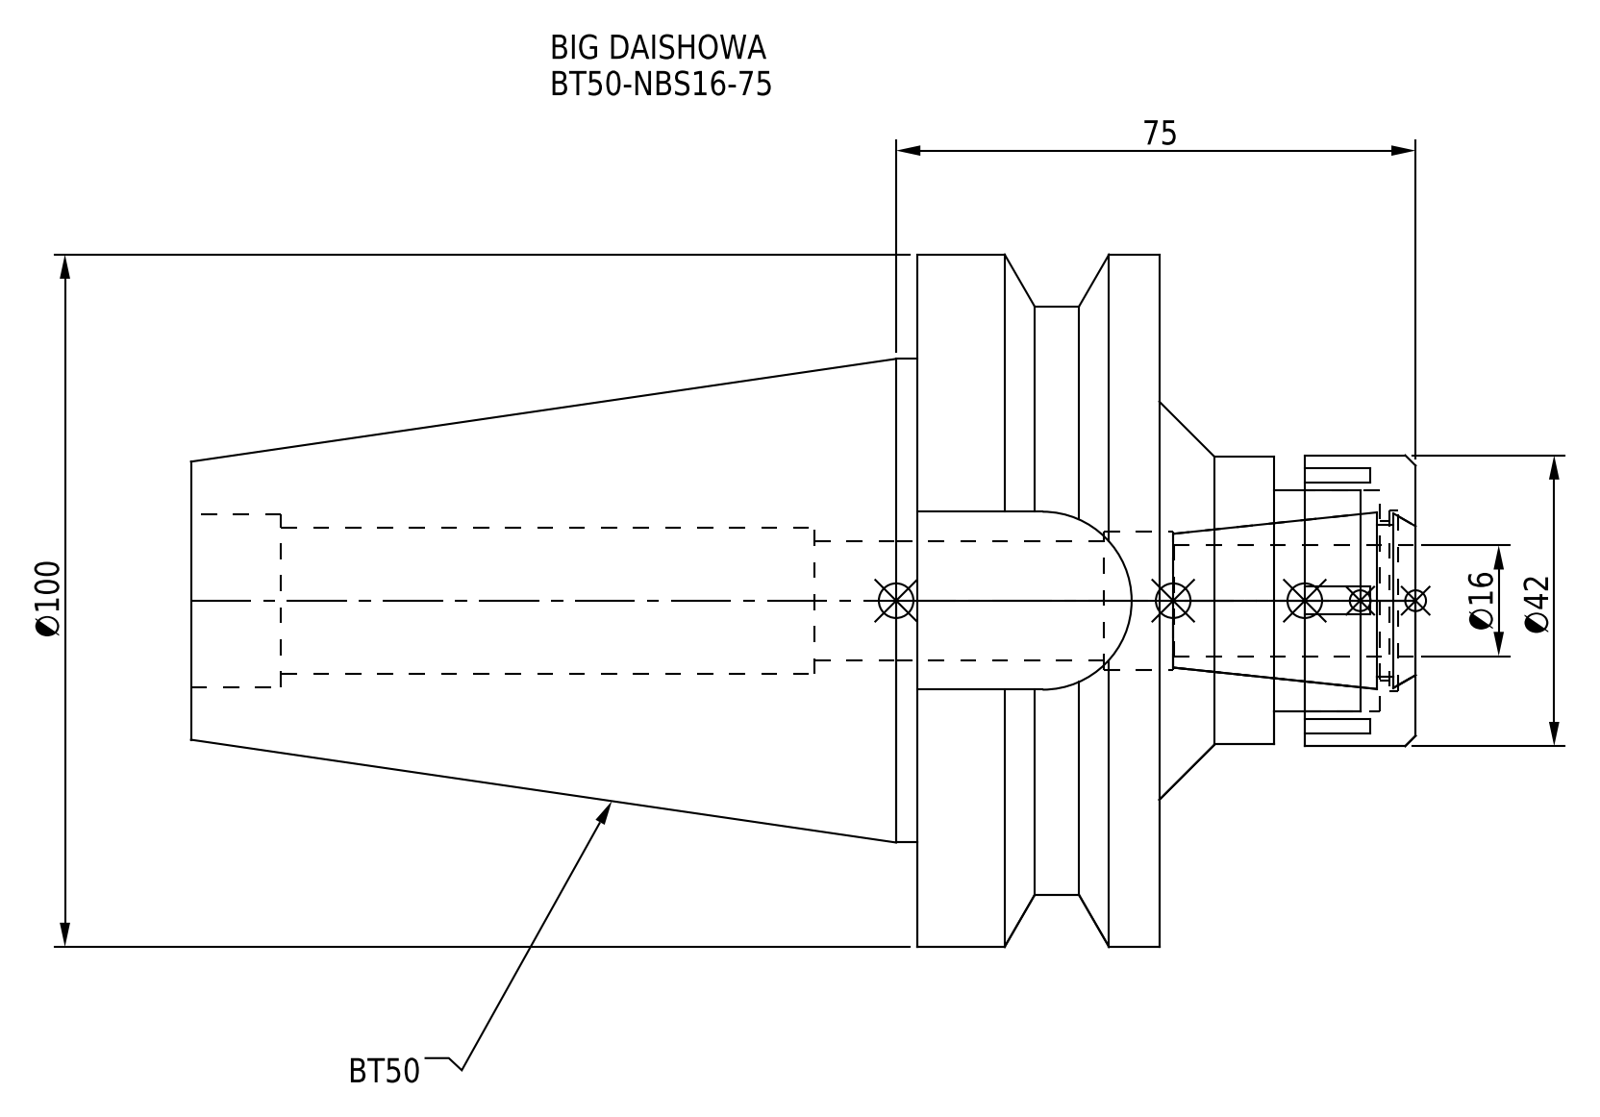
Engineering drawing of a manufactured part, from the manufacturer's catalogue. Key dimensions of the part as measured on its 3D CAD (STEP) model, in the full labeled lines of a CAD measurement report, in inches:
Part name (STEP PRODUCT): DXF_TEMP_ASSY_ASM_4_ASM.stp; NBN16_1.stp; BT50-NBS16-75_2.stp; BT50-NBS16-75 (+3 more)
STEP written by: SolidWorks 2019 (CONFIG_CONTROL_DESIGN)
Units: inches
Bodies: 2 solids, 90 faces (44 planar, 32 cylindrical, 14 other)
Overall size (bounding box): 6.961 × 3.937 × 3.937
Volume: 29.57 in³ · Surface area: 99.61 in²
Round holes (diameter × count): ⌀0.681 ×1, ⌀0.787 ×1, ⌀0.835 ×1, ⌀0.906 ×1, ⌀0.984 ×1, ⌀1.024 ×1, ⌀1.26 ×1
Round bosses / shafts (diameter × count): ⌀3.937 ×1, ⌀3.346 ×1, ⌀2.75 ×1, ⌀1.654 ×1, ⌀1.634 ×1
Partial cylindrical surfaces — rounded edges, fillets, slot ends (radius × count): R0.506 ×1
Main face-to-face distances: 1.378, 1.457, 2.787, 2.835, 6.961, 5.504, 4.126, 0.315, 0.807, 0.65
